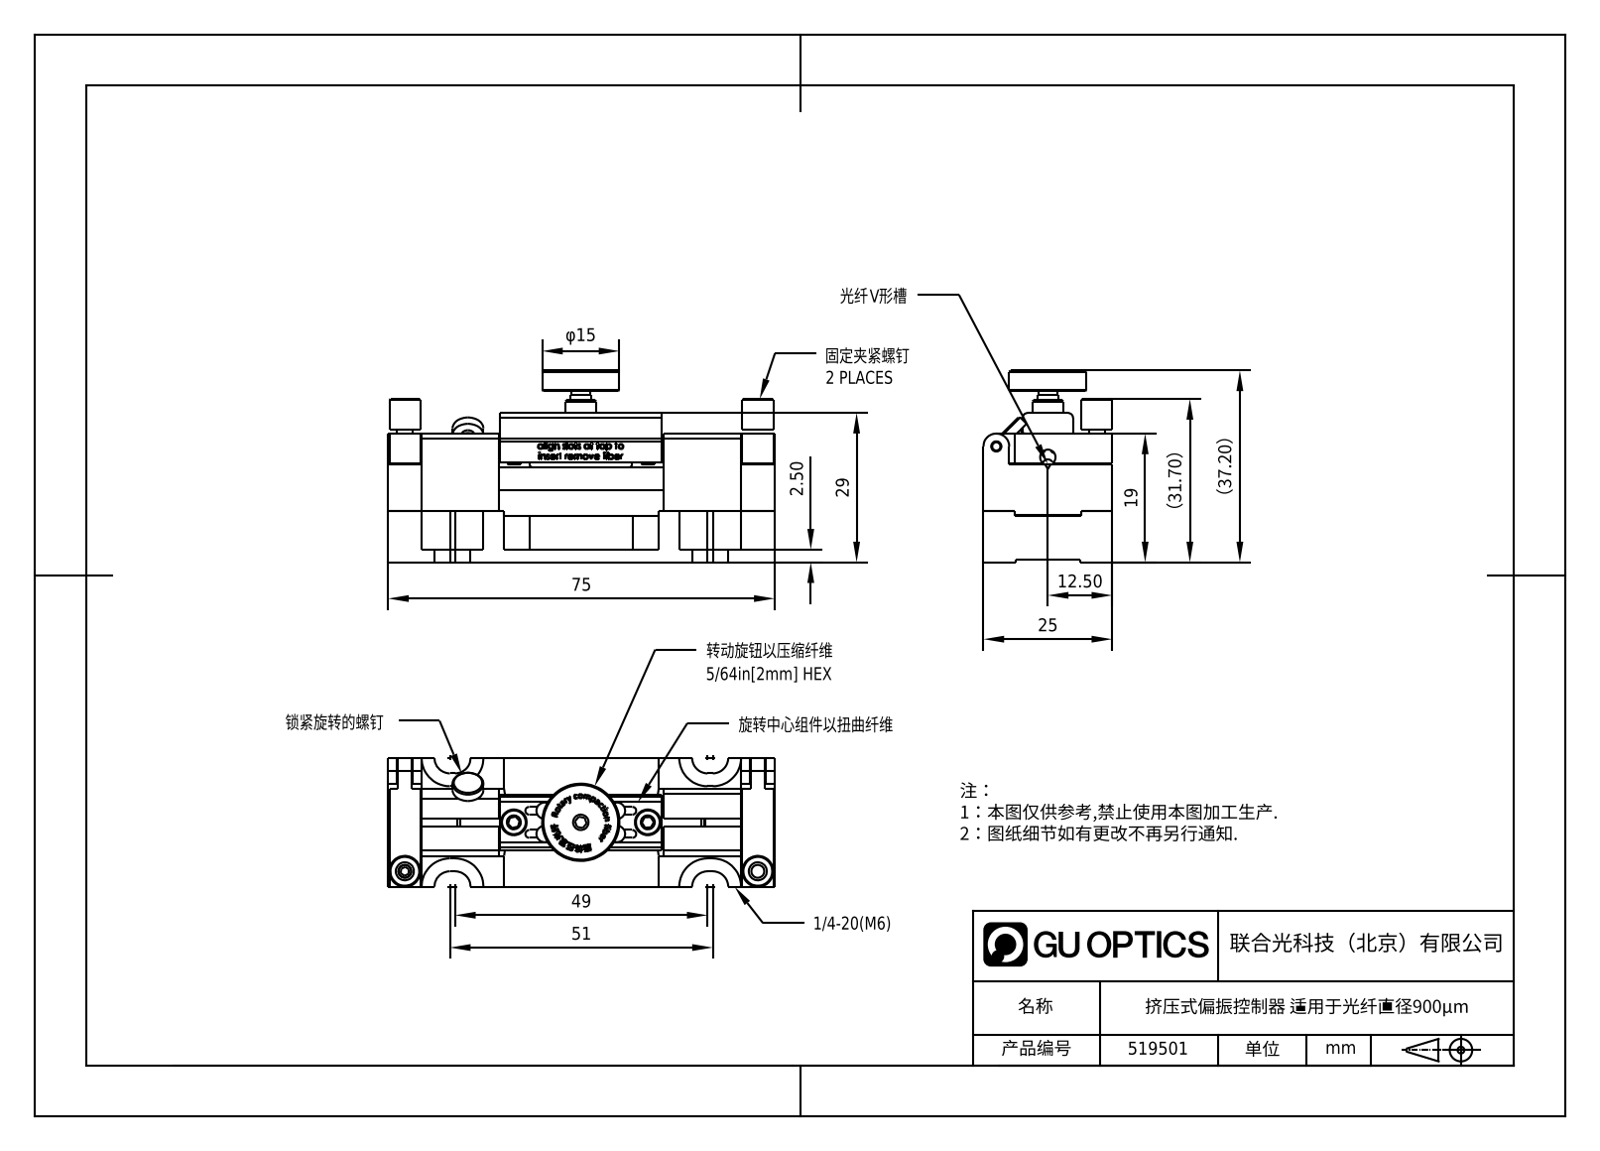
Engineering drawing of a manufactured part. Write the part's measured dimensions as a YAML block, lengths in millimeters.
part_name: "519501"
step_written_by: "SolidWorks 2020 (CONFIG_CONTROL_DESIGN)"
units: millimeters
bodies: {solids: 0, faces: 374, planar: 244, cylindrical: 79, other: 51}
overall_size: [75, 42.3, 25]
round_holes:
  - {diameter: 5, count: 4}
  - {diameter: 1.99, count: 1}
  - {diameter: 2.5, count: 1}
  - {diameter: 3.5, count: 1}
  - {diameter: 6, count: 1}
round_bosses_or_shafts:
  - {diameter: 5, count: 5}
  - {diameter: 3.2, count: 4}
  - {diameter: 2.5, count: 3}
  - {diameter: 1.5, count: 3}
  - {diameter: 10, count: 2}
  - {diameter: 12, count: 1}
  - {diameter: 6, count: 1}
  - {diameter: 4, count: 1}
partial_cylinders:
  - {radius: 0.75, count: 10}
  - {radius: 3, count: 8}
  - {radius: 5.5, count: 8}
  - {radius: 1, count: 4}
  - {radius: 5, count: 4}
  - {radius: 0.4, count: 2}
  - {radius: 2.5, count: 2}
  - {radius: 1.5, count: 1}
face_to_face_distances: [6.5, 0.5, 19, 6, 68.5, 8.5, 1, 9, 2.5, 25]
hole_center_spacings: [8, 60.5, 5.25, 13.25, 21.1, 26.15, 26.35, 34.15]
